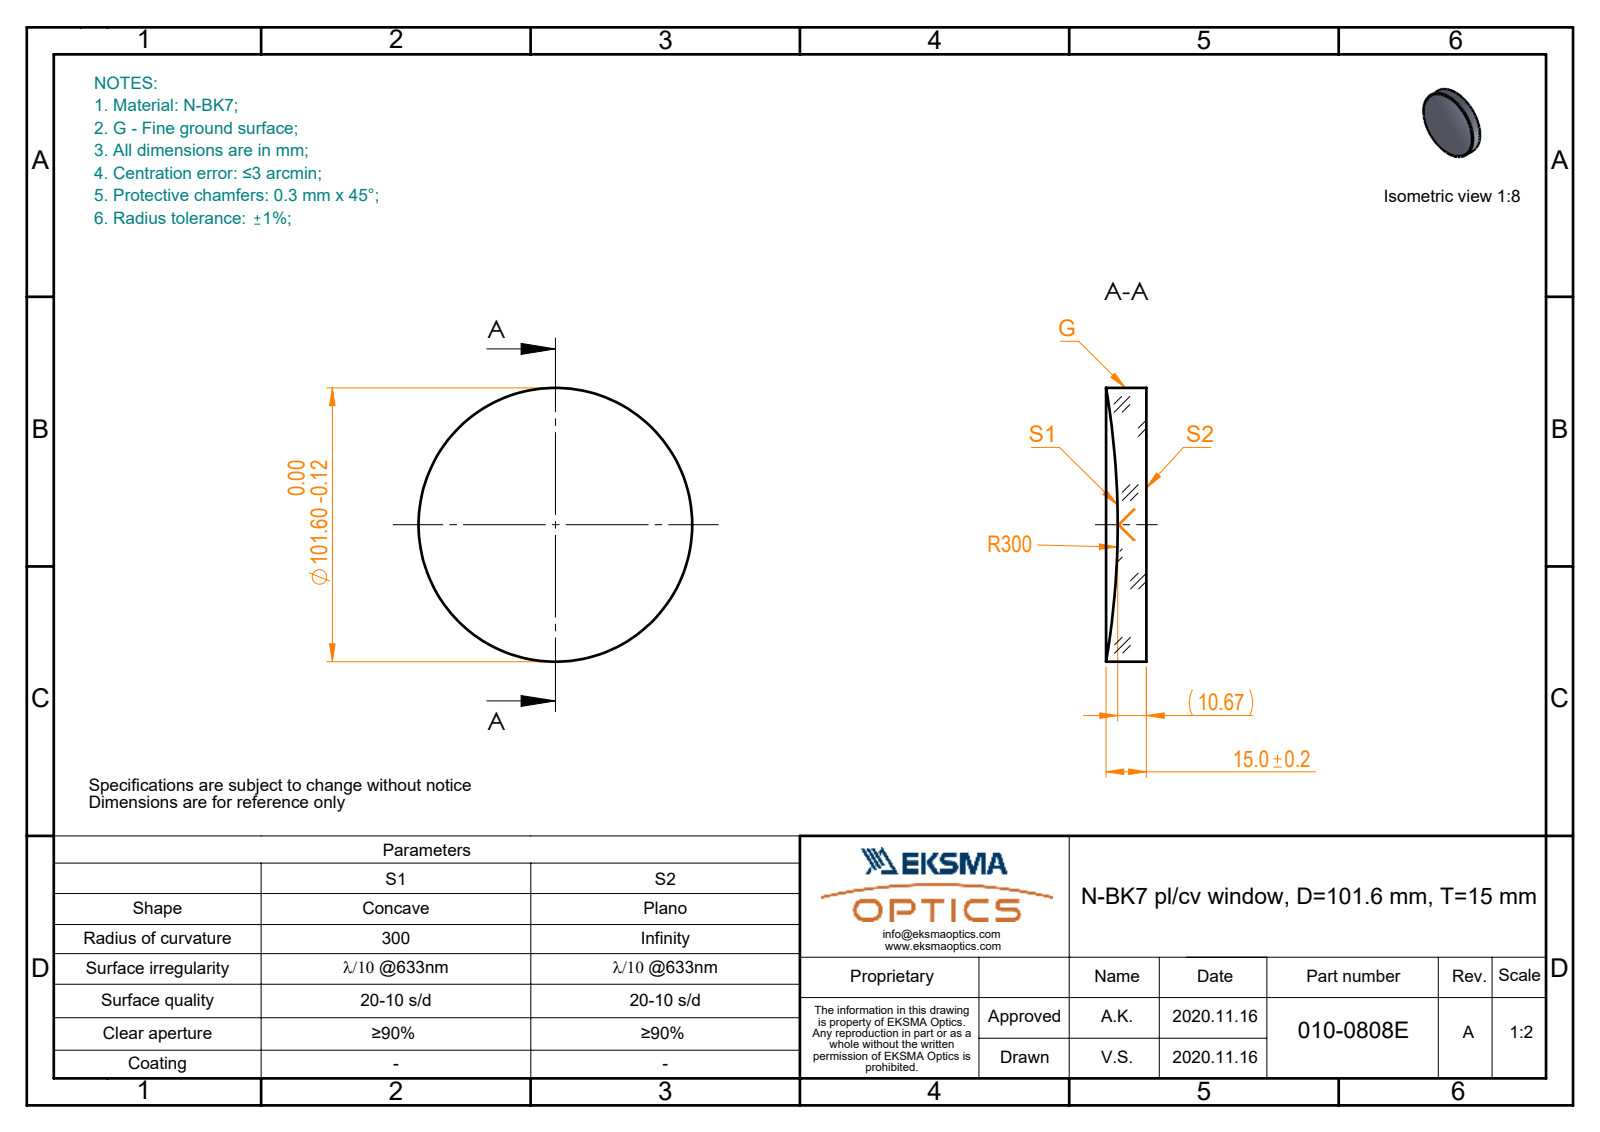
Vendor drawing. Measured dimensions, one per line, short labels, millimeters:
name: 010-0808E_N-BK7_PCV_window
written by: SolidWorks 2019 (CONFIG_CONTROL_DESIGN)
unit: mm
bodies: 1 solid, 5 faces (1 planar, 2 cylindrical, 2 other)
size: 101.6 × 101.6 × 15
volume: 104 005 mm³; area: 21 061 mm²
bosses: 1× ⌀101.6
